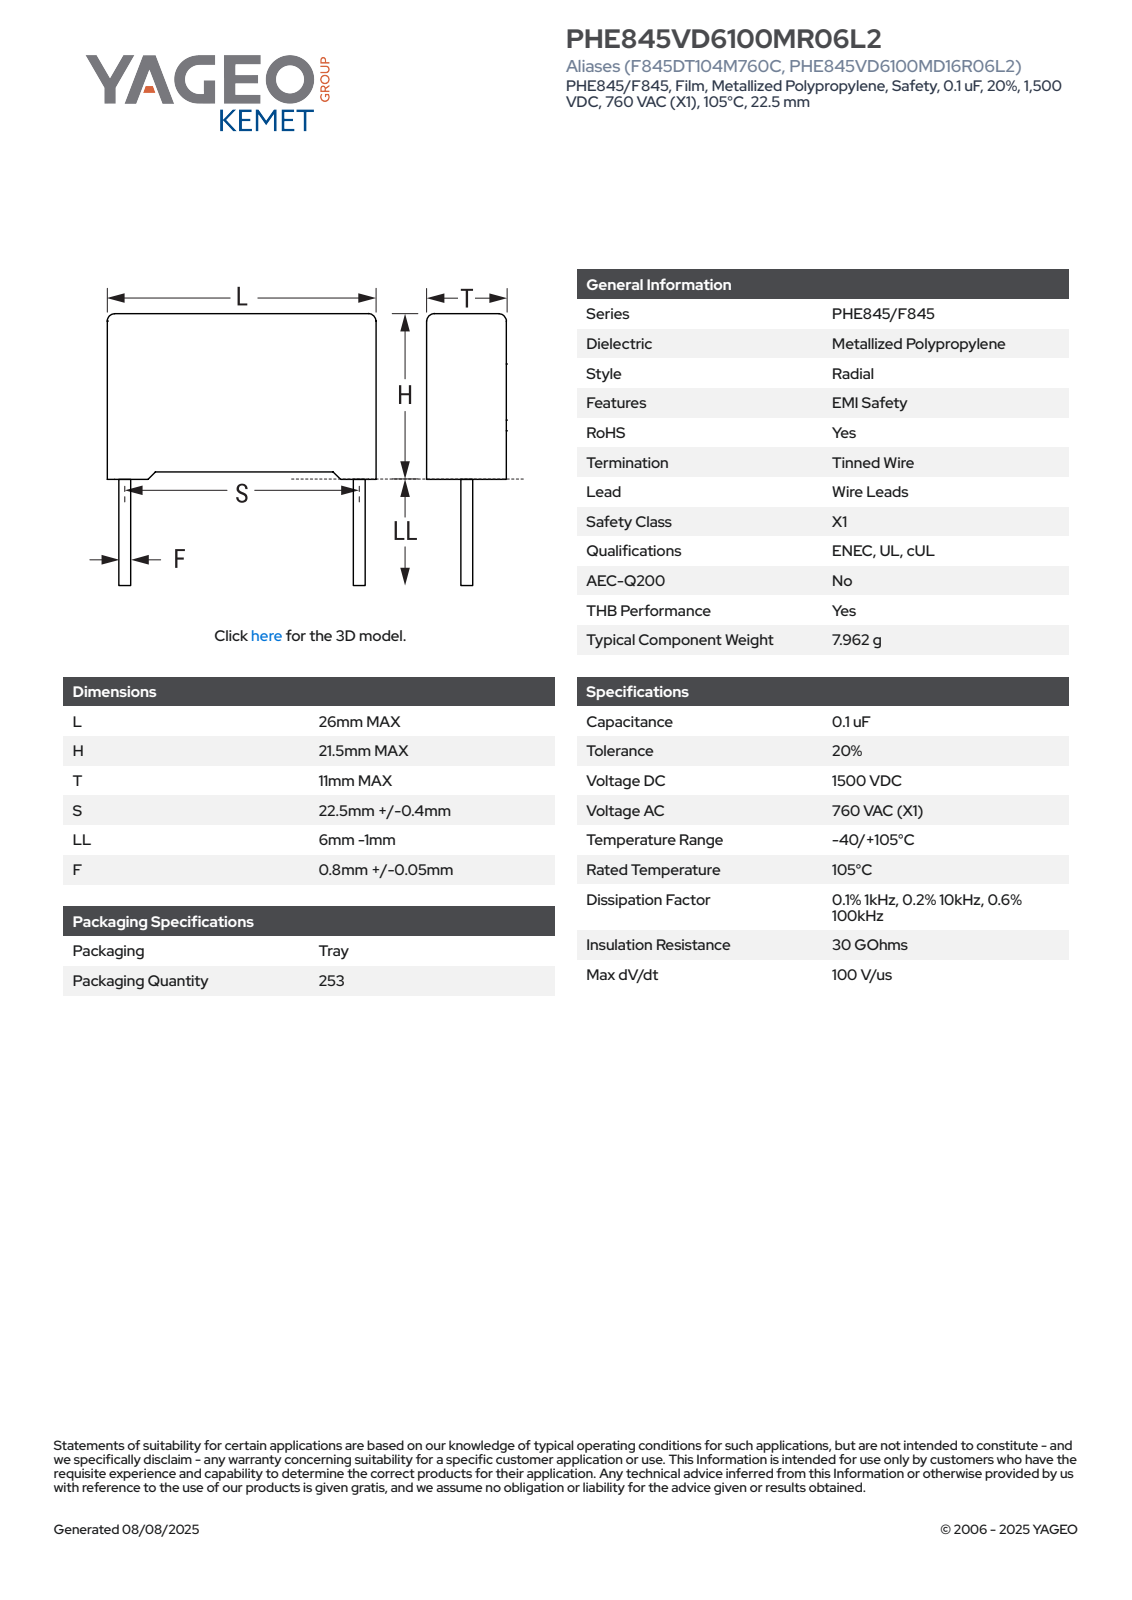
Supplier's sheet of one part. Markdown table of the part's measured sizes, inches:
| quantity | value |
| --- | --- |
| part name | CFR_RB2_26X21.5X11_L26H21.5T11S22.5LL5F0.8 |
| STEP written by | SolidWorks 2021 (AUTOMOTIVE_DESIGN) |
| units | inches |
| bodies | 4 solids, 85 faces (77 planar, 8 cylindrical, 0 other) |
| overall size | 1.043 × 1.024 × 0.433 |
| volume | 0.364 in³ |
| surface area | 3.444 in² |
| round bosses / shafts (diameter × count) | 0.031 × 2 |
| partial cylindrical surfaces (radius × count) | 0.02 × 4 |
| main face-to-face distances | 0.433, 1.024, 0.817, 0.817, 0.029, 0.03, 0.846, 0.034, 0.989, 0.399 |
